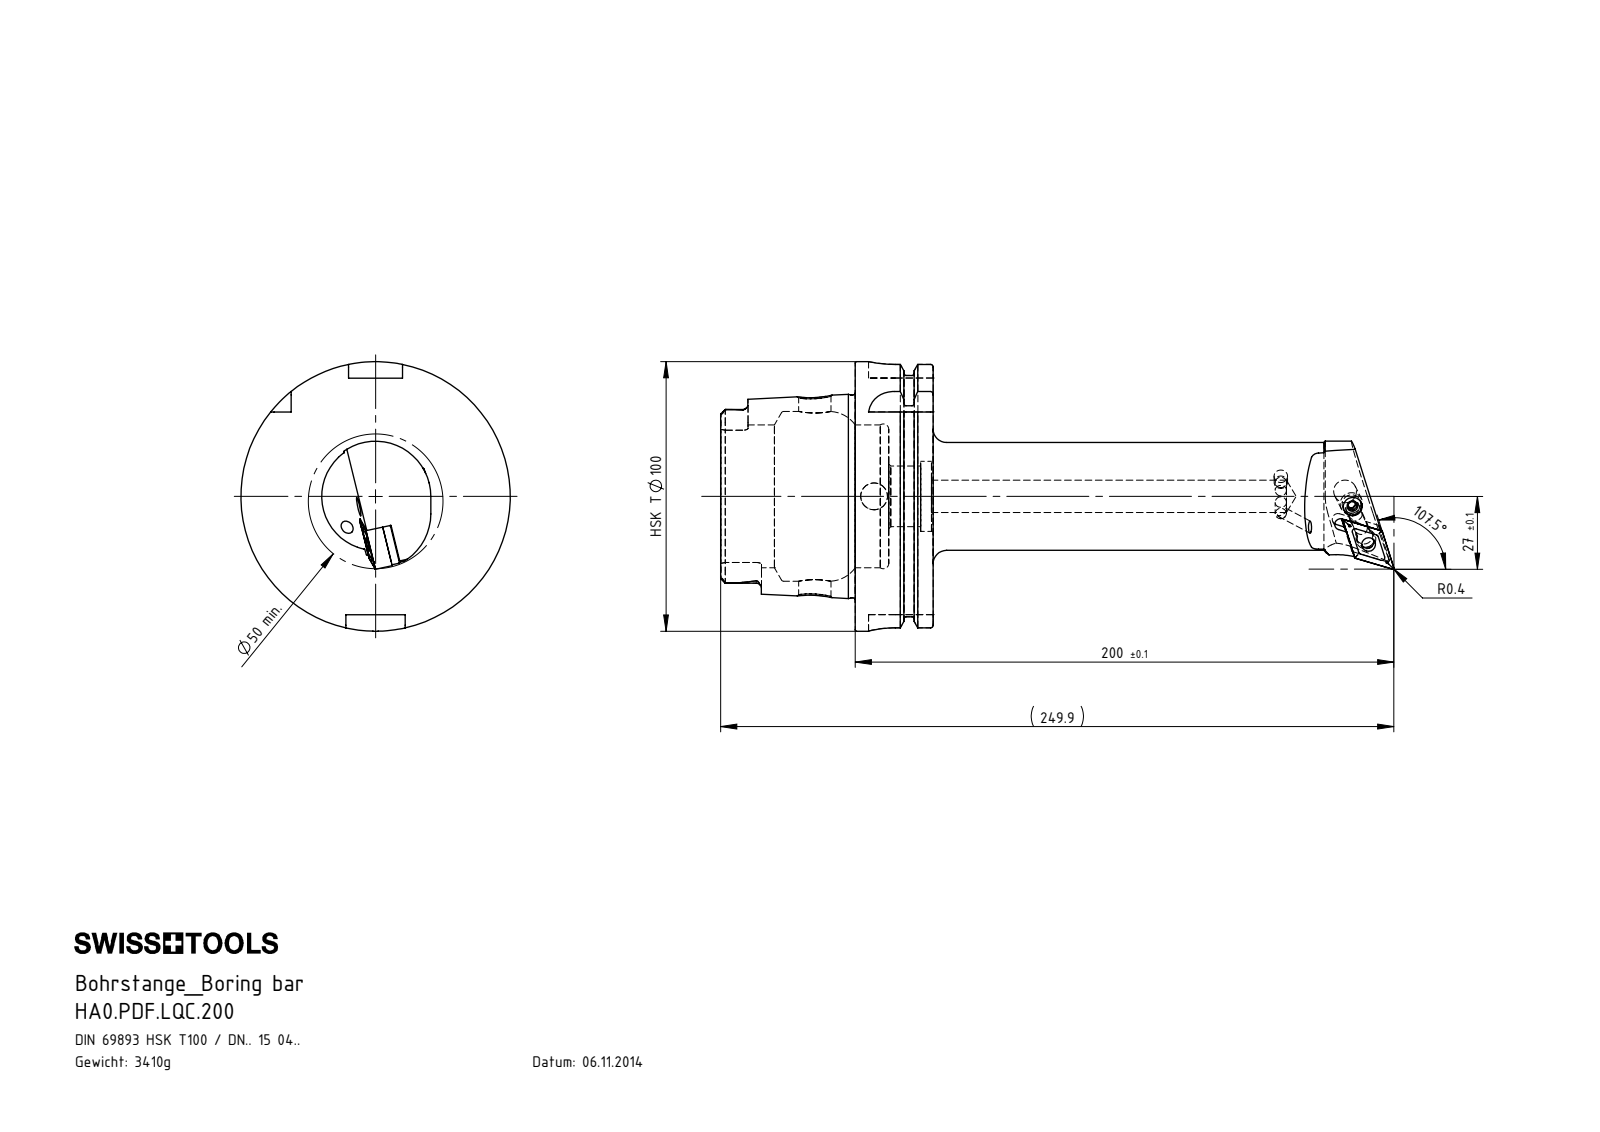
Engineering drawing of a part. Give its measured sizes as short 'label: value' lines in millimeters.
name: HA0-PDF.LQC.200; WDF-ER3.101.000_A; WCD-ER4.101.017_A; KVT_MB_600_060 (+3 more)
written by: SolidWorks 2012 (AUTOMOTIVE_DESIGN)
unit: mm
bodies: 7 solids, 359 faces (109 planar, 102 cylindrical, 148 other)
size: 249.9 × 100 × 100
volume: 435 362 mm³; area: 78 915 mm²
holes: 2× ⌀5, 2× ⌀12, 1× ⌀4, 1× ⌀4.2, 1× ⌀5.16, 1× ⌀6.4, 1× ⌀7, 1× ⌀8.4, 1× ⌀10, 1× ⌀22.5, 1× ⌀26, 1× ⌀53
bosses: 1× ⌀100, 1× ⌀91.95, 1× ⌀75.26, 1× ⌀40, 1× ⌀8, 1× ⌀7.9, 1× ⌀6.4, 1× ⌀6
rounds: 6× R1.9, 4× R0.4, 4× R1, 4× R10, 2× R2.5, 2× R4.83, 2× R4.88, 2× R20.5
face distances: 28.95, 12.45, 16.5, 49.9, 62.35, 78.85, 87.8, 78.2, 28.3, 15.85
hole spacings: 15.62
